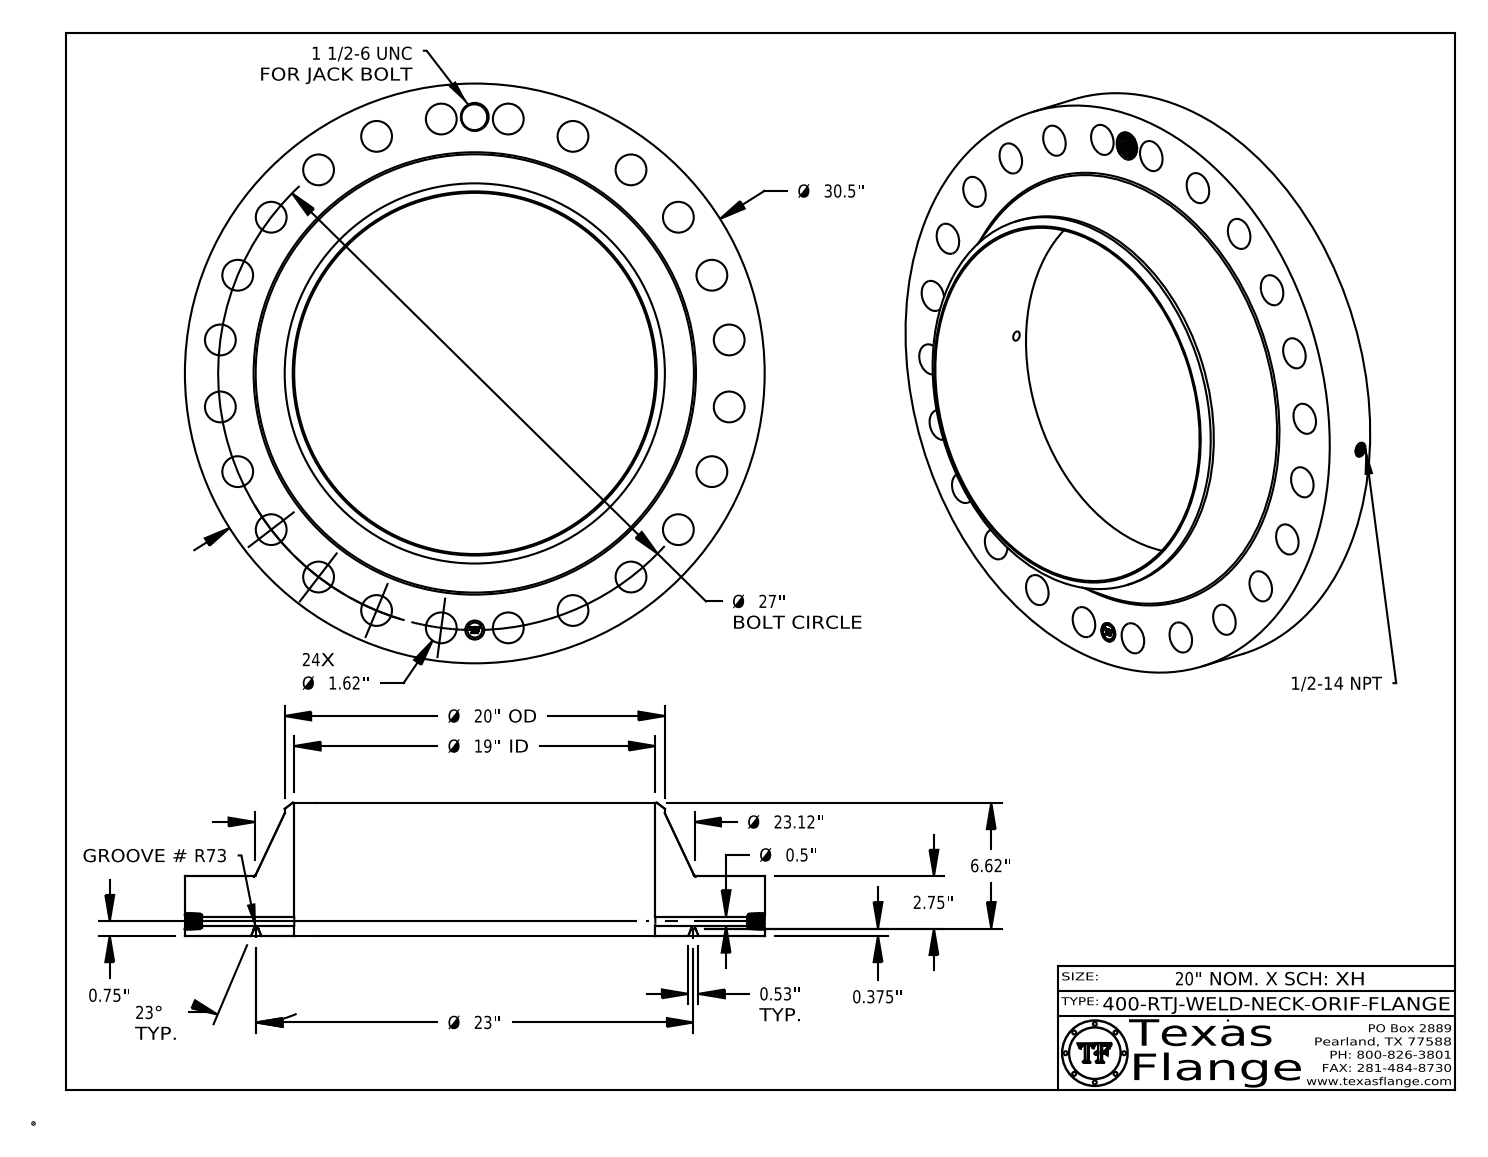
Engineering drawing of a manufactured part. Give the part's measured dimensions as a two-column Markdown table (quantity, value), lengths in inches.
| quantity | value |
| --- | --- |
| part name | 400-RTJ-WELD-NECK |
| STEP written by | CATIA V5 STEP AP214 (AUTOMOTIVE_DESIGN) |
| units | inches |
| bodies | 1 solid, 831 faces (370 planar, 131 cylindrical, 330 other) |
| overall size | 30.5 × 30.5 × 6.995 |
| volume | 1 510 in³ |
| surface area | 2 129 in² |
| round holes (diameter × count) | 1.62 × 24, 0.5 × 1, 0.672 × 1, 1 × 1, 1.344 × 1, 19 × 1 |
| round bosses / shafts (diameter × count) | 0.061 × 8, 30.5 × 1, 20 × 1, 0.788 × 1 |
| main face-to-face distances | 3.125, 0.375, 2.75, 6.995, 6.62, 3.87, 0.015, 3.11, 2.735, 3.885 |
| hole center spacings | 13.5, 23.383, 24.945, 21.42, 3.524, 6.988, 19.092, 26.08 |
